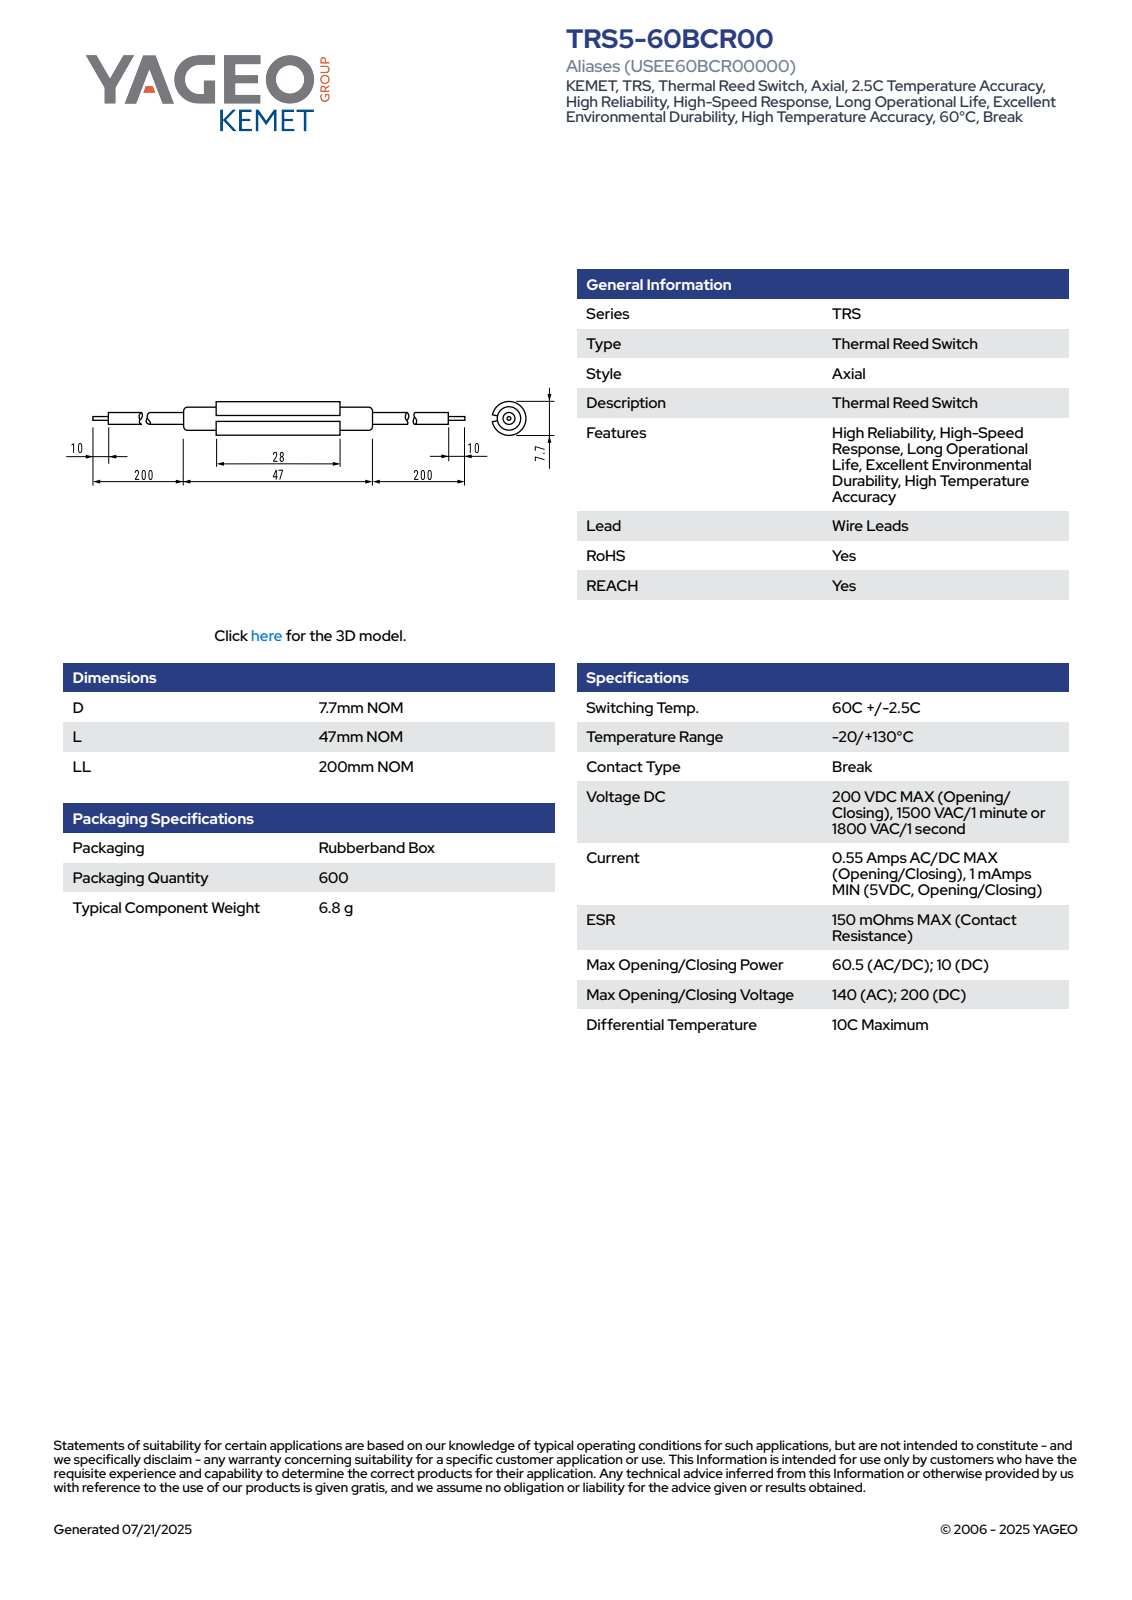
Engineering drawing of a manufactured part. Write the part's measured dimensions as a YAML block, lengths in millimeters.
part_name: "Default"
step_written_by: "SolidWorks 2014 (AUTOMOTIVE_DESIGN)"
units: millimeters
bodies: {solids: 1, faces: 86, planar: 32, cylindrical: 15, other: 39}
overall_size: [447, 7.71, 7.63]
volume: 4093
surface_area: 4510
round_bosses_or_shafts:
  - {diameter: 7.7, count: 1}
  - {diameter: 5.7, count: 1}
  - {diameter: 2.8, count: 1}
  - {diameter: 0.5, count: 1}
partial_cylinders:
  - {radius: 3.86, count: 1}
face_to_face_distances: [9.5, 37.5, 190, 199.5, 227.5, 237, 47, 28, 427, 10]
